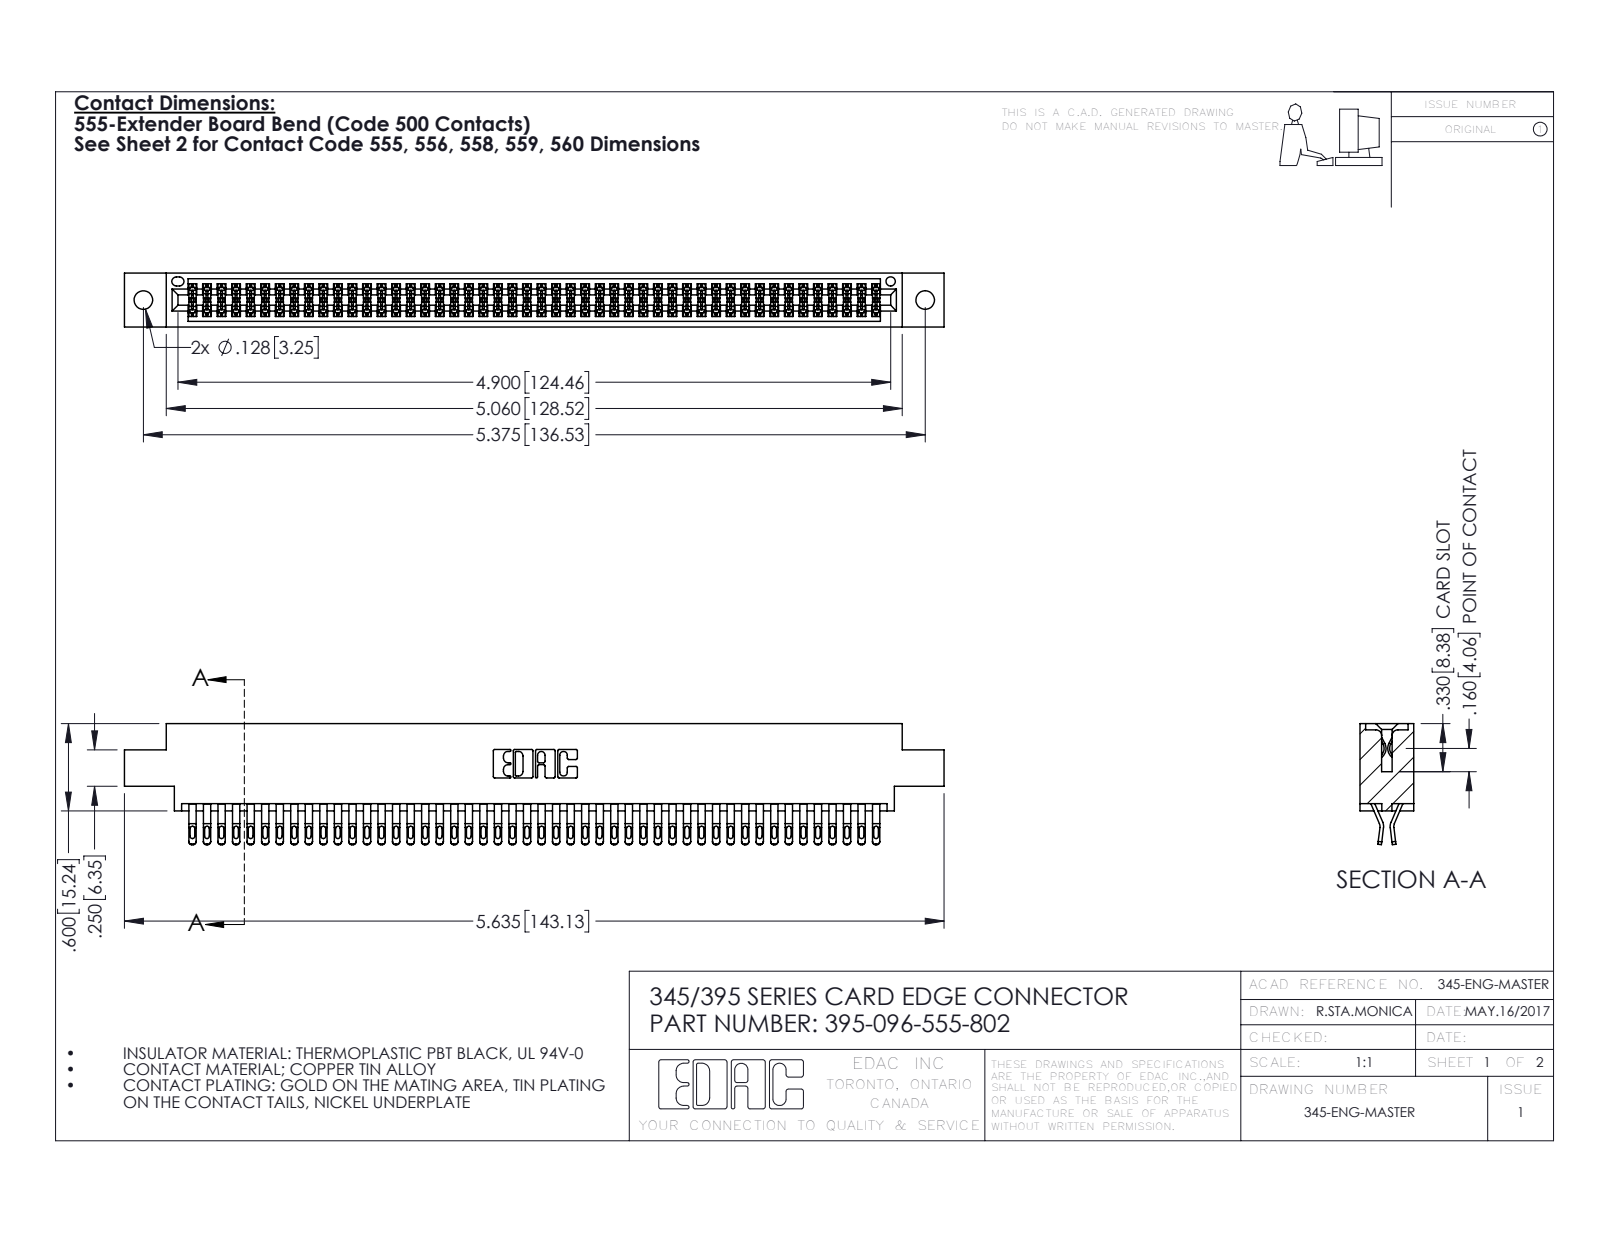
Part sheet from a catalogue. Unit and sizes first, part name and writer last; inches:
Units: inches
Overall size (bounding box): 5.635 × 0.832 × 0.37
Round holes (diameter × count): ⌀0.128 ×2, ⌀0.064 ×1
Partial cylindrical surfaces — rounded edges, fillets, slot ends (radius × count): R0.016 ×240, R0.02 ×192, R0.006 ×144, R0.01 ×22, R0.007 ×6, R0.031 ×6, R0.026 ×3, R0.01 ×2
Main face-to-face distances: 0.298, 0.072, 0.37, 0.025, 0.2, 0.098, 0.272, 0.225, 0.175, 0.149
Hole centre spacings: 0.27, 5.139, 5.375
Volume: 0.86 in³ · Surface area: 33.76 in²
Bodies: 97 solids, 5506 faces (3060 planar, 2446 cylindrical, 0 other)
Part name (STEP PRODUCT): 345-292-001_555 Tail; 345 Part_0.170 Offset - 0.128 Dia; 395-096-555-802
STEP written by: SolidWorks 2016 (CONFIG_CONTROL_DESIGN)
